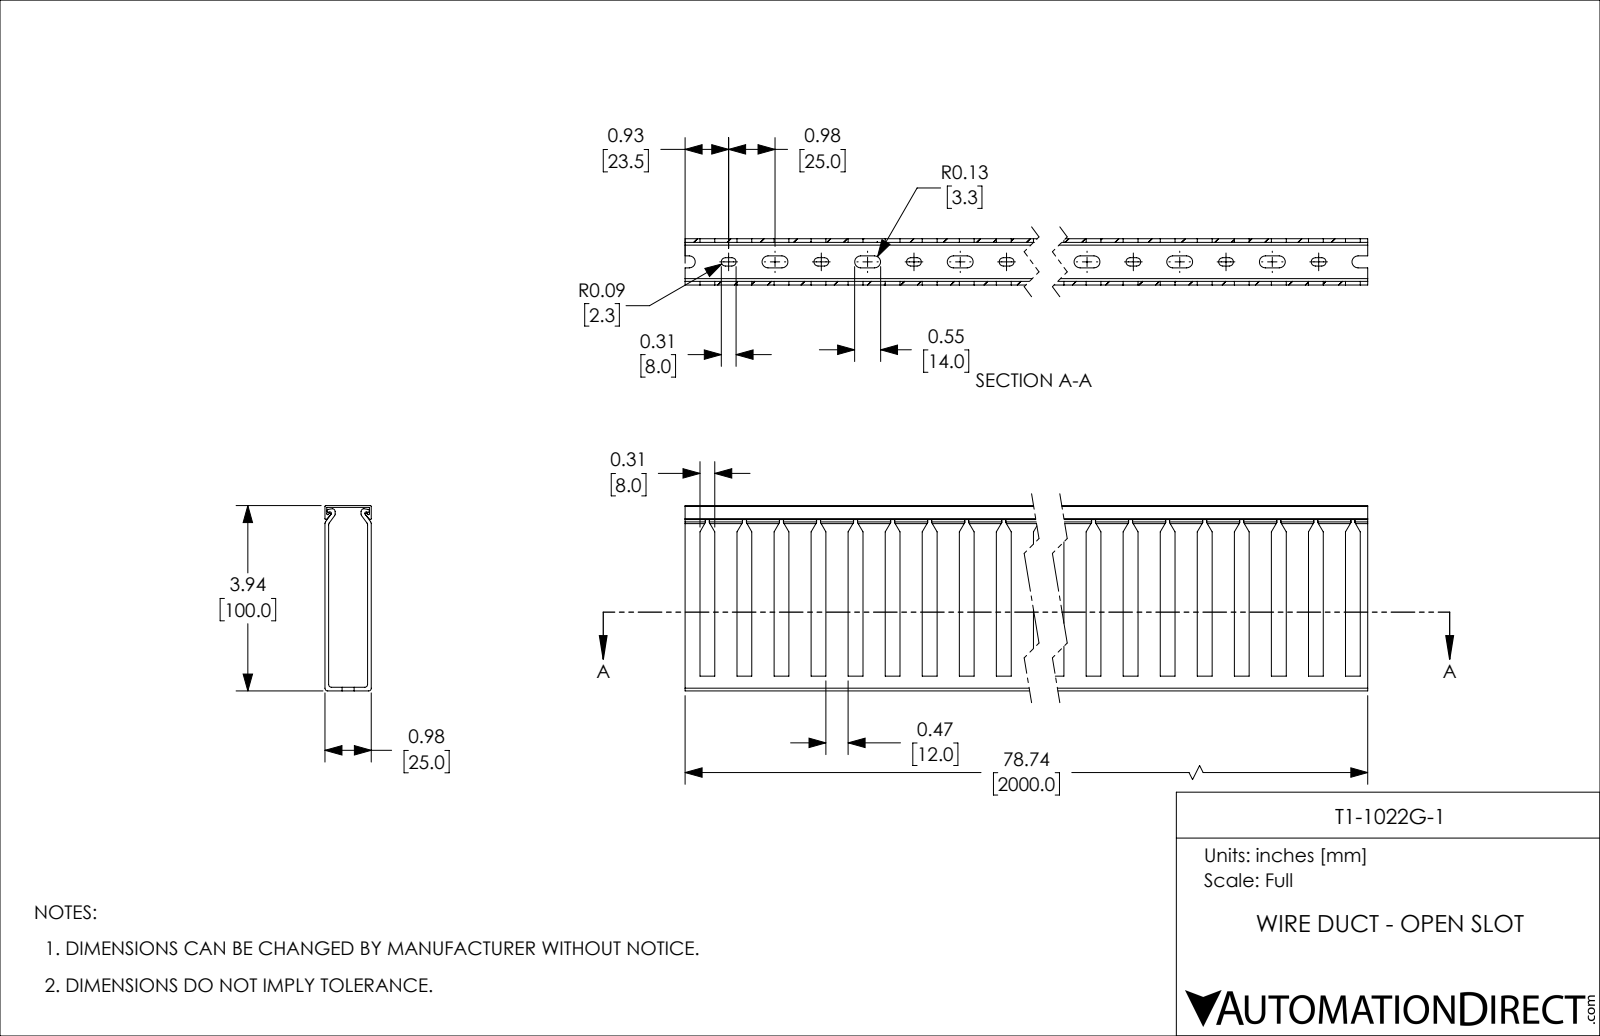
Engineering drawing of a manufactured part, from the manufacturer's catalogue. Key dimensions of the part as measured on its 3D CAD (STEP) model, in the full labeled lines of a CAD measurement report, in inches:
Part name (STEP PRODUCT): T1-1040W-1
STEP written by: SolidWorks 2021 (CONFIG_CONTROL_DESIGN)
Units: inches
Bodies: 2 solids, 945 faces (514 planar, 431 cylindrical, 0 other)
Overall size (bounding box): 78.74 × 3.937 × 0.984
Volume: 57.58 in³ · Surface area: 1 610 in²
Partial cylindrical surfaces — rounded edges, fillets, slot ends (radius × count): R0.089 ×80, R0.128 ×80, R0.059 ×12, R0.02 ×8, R0.03 ×6
Main face-to-face distances: 0.079, 0.906, 0.984, 0.827, 0.039, 3.937, 3.898, 3.819, 3.858, 0.945
